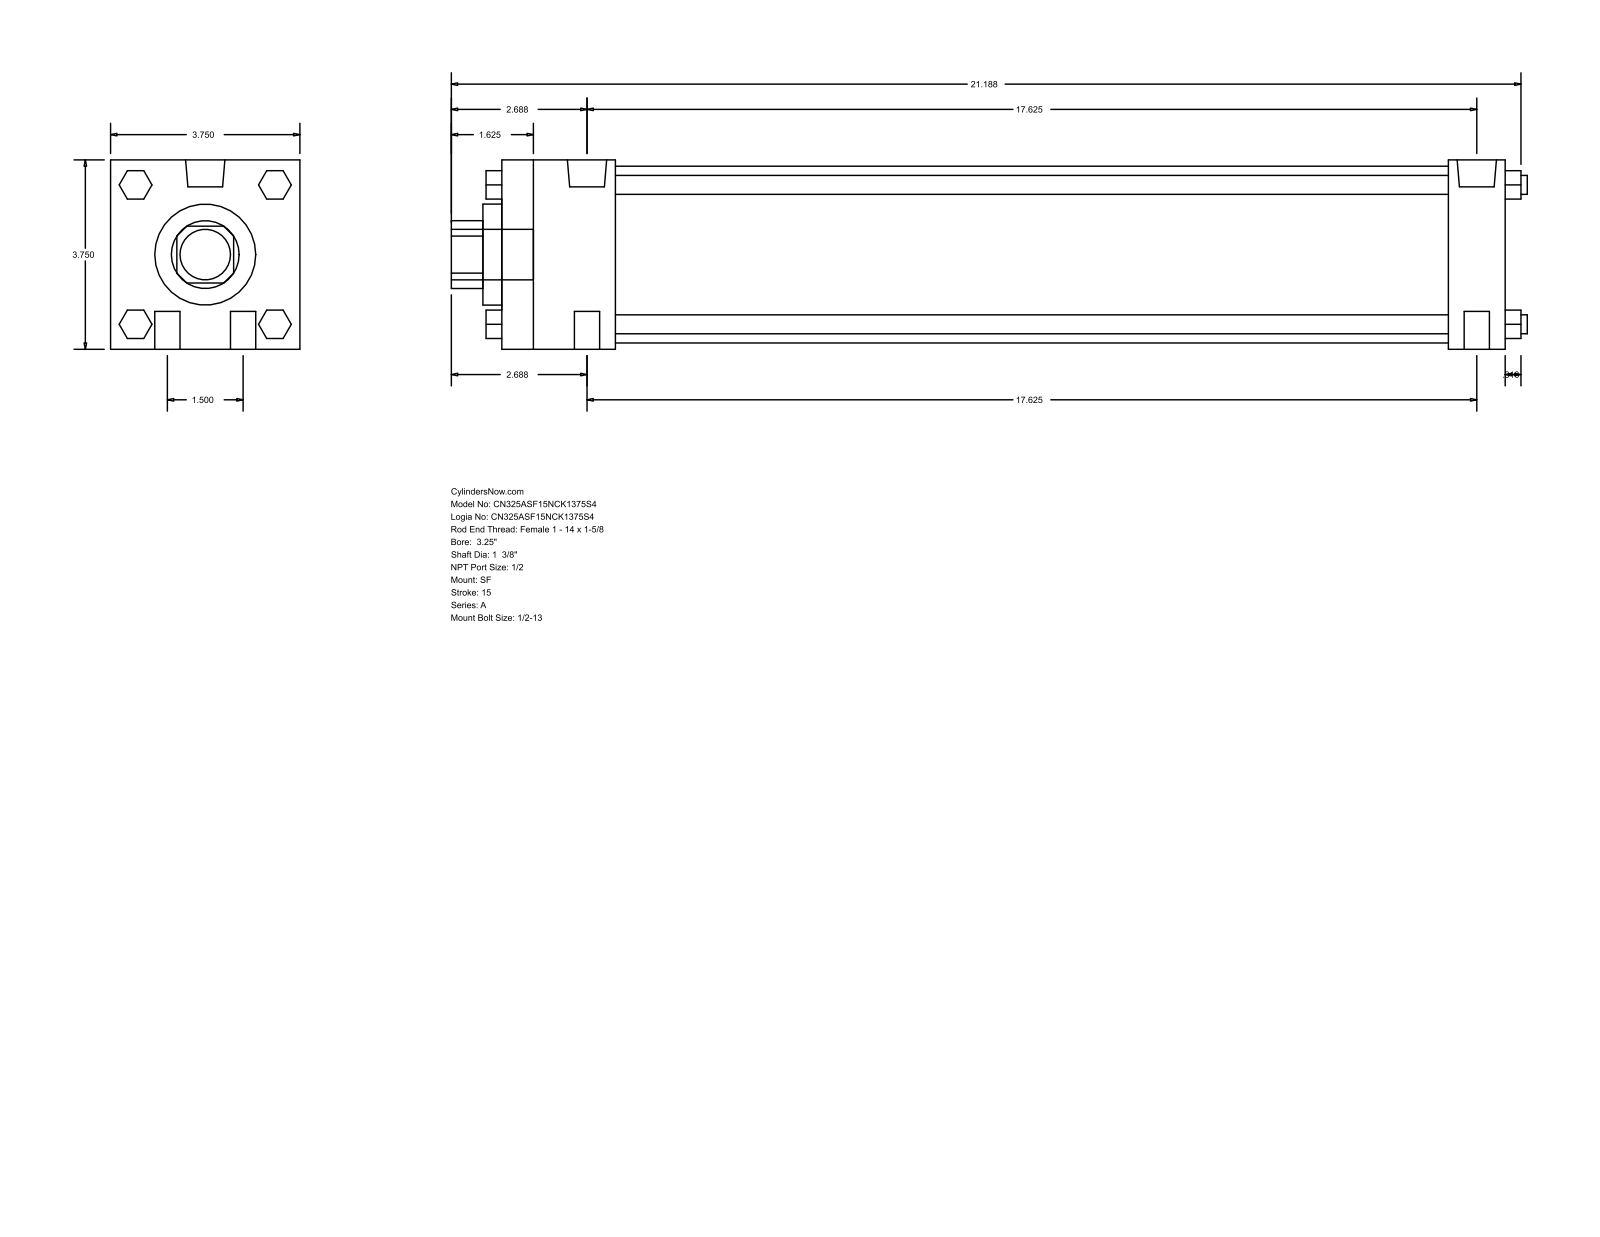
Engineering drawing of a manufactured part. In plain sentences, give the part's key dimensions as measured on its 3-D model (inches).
The part is named "A_SF__0325_1.375". Its 3-D file was written by "GSSL Pune (CONFIG_CONTROL_DESIGN)". It is 0 solids with 124 faces: 94 planar, 30 cylindrical and 0 other. Overall it measures 21.313 by 3.75 by 3.75 inches. Round holes: 1 of diameter 1.375, 1 of diameter 2, 1 of diameter 3.5. Round bosses or shafts: 4 of diameter 0.5, 4 of diameter 0.375, 2 of diameter 0.778, 2 of diameter 0.344, 1 of diameter 1. Partial cylindrical surfaces (rounded edges, fillets, slot ends): 1 of radius 0.672. The main face-to-face distances are 3.75, 19.875, 1.125, 18.75, 2.25, 16.5, 17.625, 0.375, 2.625, 19.125.
